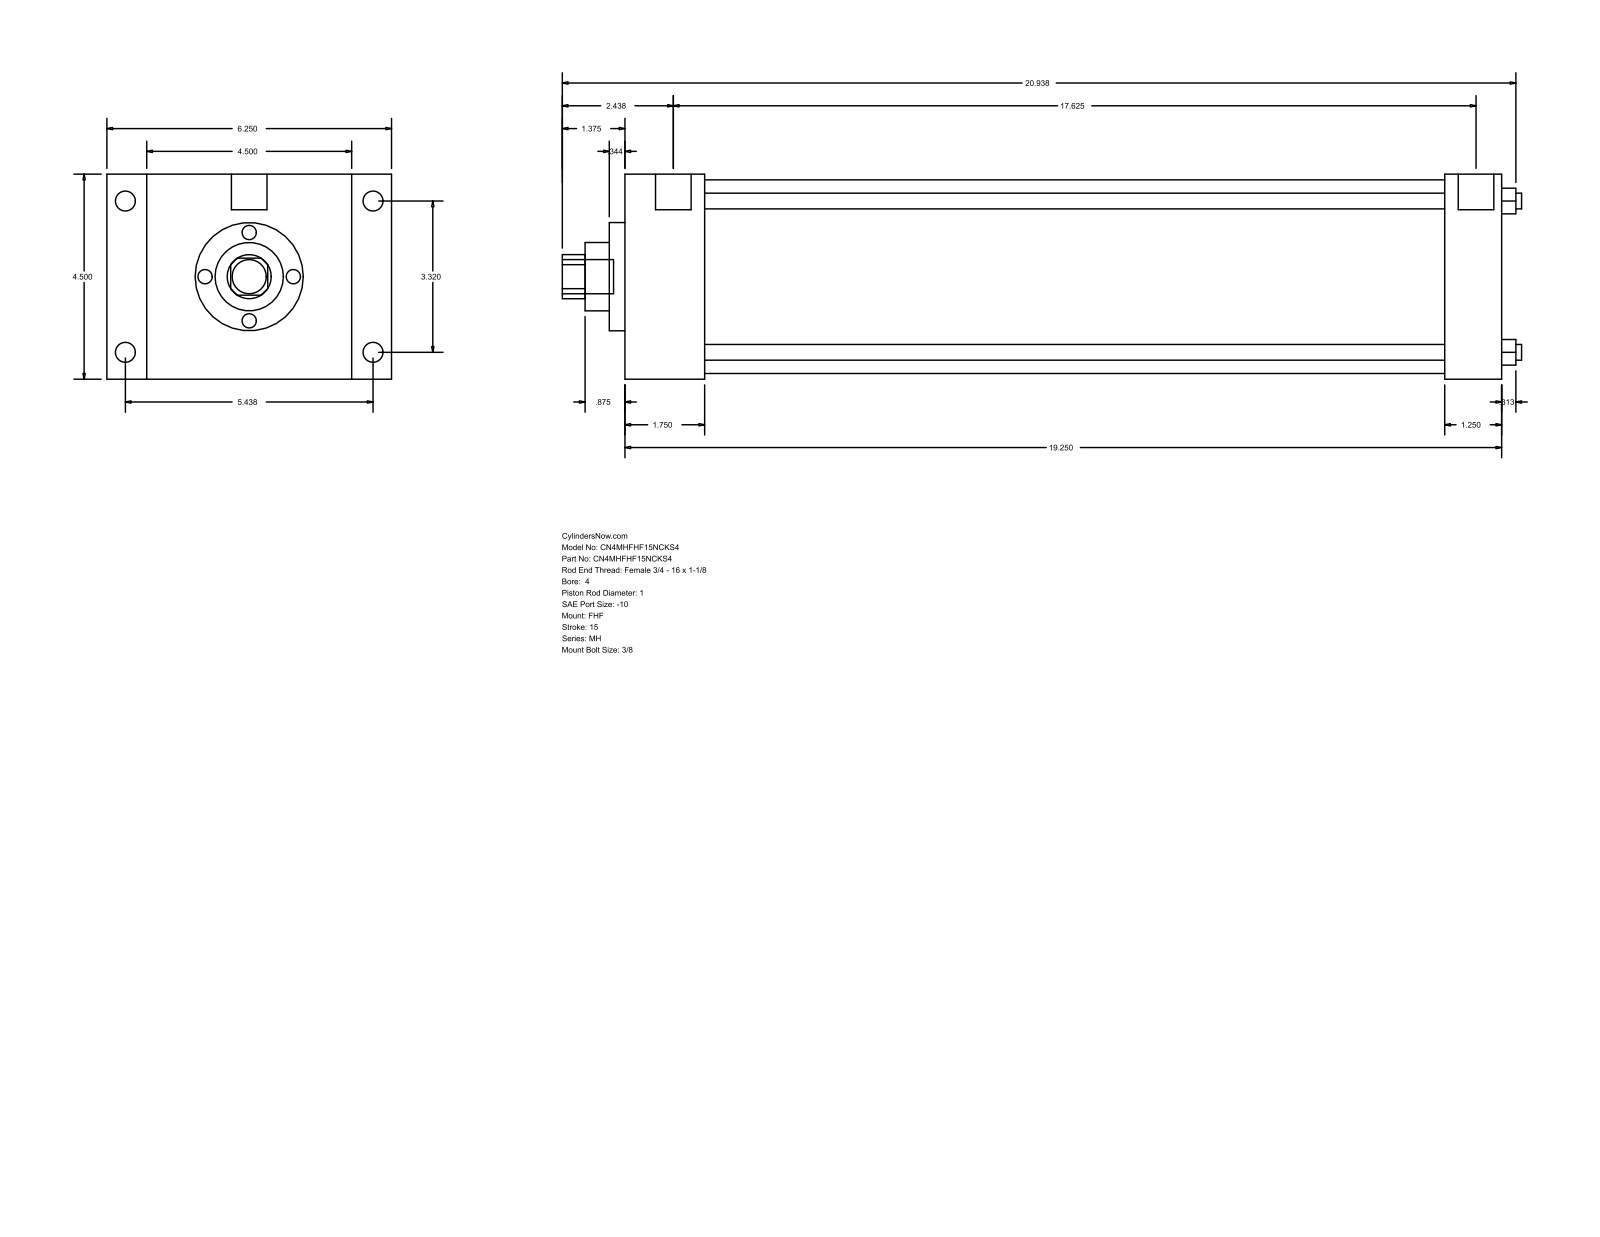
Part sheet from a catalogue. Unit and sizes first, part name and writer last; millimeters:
Units: millimetres
Overall size (bounding box): 534.99 × 158.75 × 114.3
Round holes (diameter × count): ⌀8.76 ×4, ⌀25.4 ×1, ⌀38.1 ×1, ⌀60.33 ×1, ⌀107.95 ×1
Round bosses / shafts (diameter × count): ⌀11.13 ×4, ⌀8.73 ×4, ⌀19.84 ×2, ⌀19.05 ×1
Partial cylindrical surfaces — rounded edges, fillets, slot ends (radius × count): R12.29 ×1
Main face-to-face distances: 114.3, 488.96, 44.46, 444.5, 22.23, 136.53, 158.76, 457.2, 412.74, 31.76
Hole centre spacings: 59.62, 84.32, 119.25
Bodies: 0 solids, 90 faces (61 planar, 29 cylindrical, 0 other)
Part name (STEP PRODUCT): MH_FHF__0400_1
STEP written by: GSSL Pune (CONFIG_CONTROL_DESIGN)
